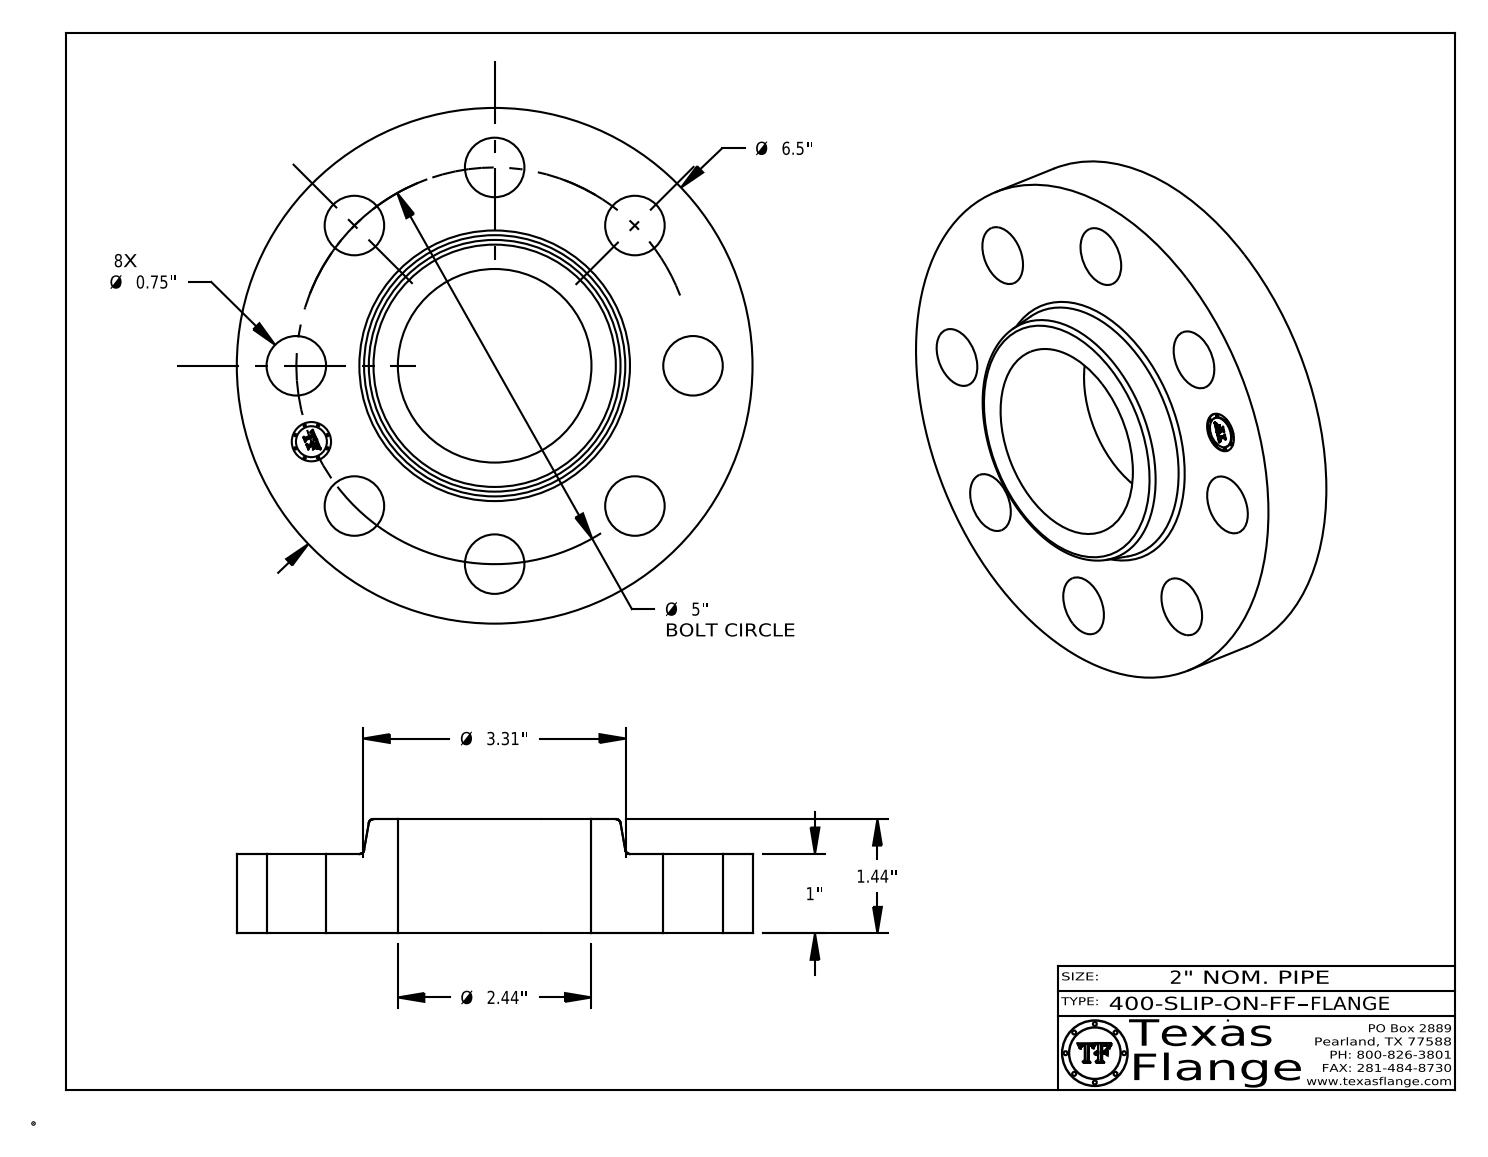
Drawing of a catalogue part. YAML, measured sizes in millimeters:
part_name: "400-SLIP-ON-FF"
step_written_by: "CATIA V5 STEP AP214 (AUTOMOTIVE_DESIGN)"
units: millimeters
bodies: {solids: 1, faces: 414, planar: 368, cylindrical: 40, other: 6}
overall_size: [165.1, 165.1, 36.6]
volume: 434700
surface_area: 66970
round_holes:
  - {diameter: 19.1, count: 8}
  - {diameter: 12.6, count: 1}
  - {diameter: 62, count: 1}
round_bosses_or_shafts:
  - {diameter: 0.8, count: 8}
  - {diameter: 165.1, count: 1}
  - {diameter: 9.9, count: 1}
face_to_face_distances: [25.4, 36.6, 11.2, 25, 0.4, 11.6, 3.8, 3.7, 0.7, 2.4]
hole_center_spacings: [63.5, 48.6, 89.8, 117.3, 127, 24.8, 70.6, 105.6]
